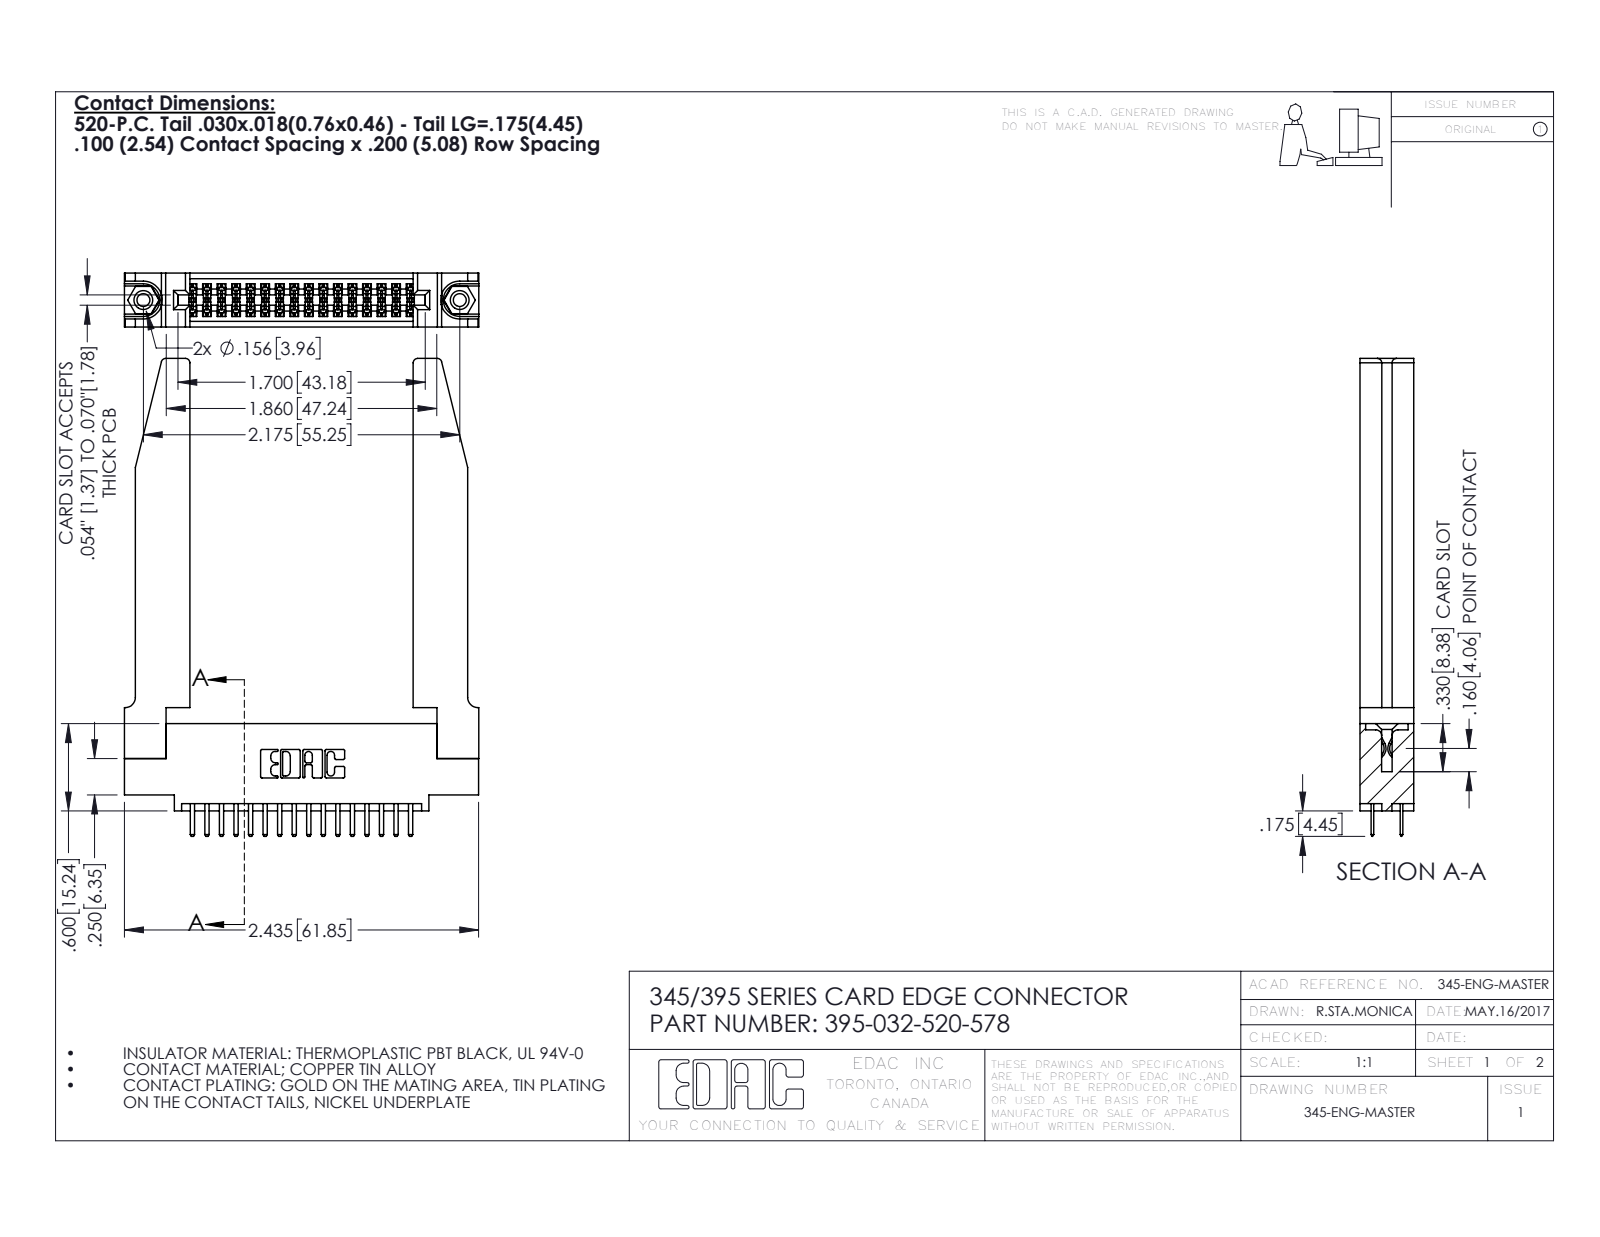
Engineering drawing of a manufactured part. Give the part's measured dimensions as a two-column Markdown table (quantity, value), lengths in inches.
| quantity | value |
| --- | --- |
| part name | 345-220-078_345-220-078; 345-250-001_345-250-001-102; 345-292-001_345-293-120; 345 Part_0.110 Offset - 0.156 Dia-TH (+1 more) |
| STEP written by | SolidWorks 2016 (CONFIG_CONTROL_DESIGN) |
| units | inches |
| bodies | 37 solids, 2092 faces (1346 planar, 694 cylindrical, 52 other) |
| overall size | 3.285 × 2.436 × 0.37 |
| volume | 0.821 in³ |
| surface area | 22.93 in² |
| round holes (diameter × count) | 0.089 × 2, 0.125 × 2, 0.156 × 2, 0.064 × 1 |
| round bosses / shafts (diameter × count) | 0.155 × 2 |
| partial cylindrical surfaces (radius × count) | 0.006 × 48, 0.01 × 36, 0.01 × 22, 0.03 × 8, 0.007 × 6, 0.031 × 6, 0.026 × 3, 0.014 × 2 |
| main face-to-face distances | 0.37, 0.072, 0.298, 0.2, 0.15, 0.22, 0.077, 0.148, 0.098, 0.272 |
| hole center spacings | 0.27, 1.942, 2.175 |
